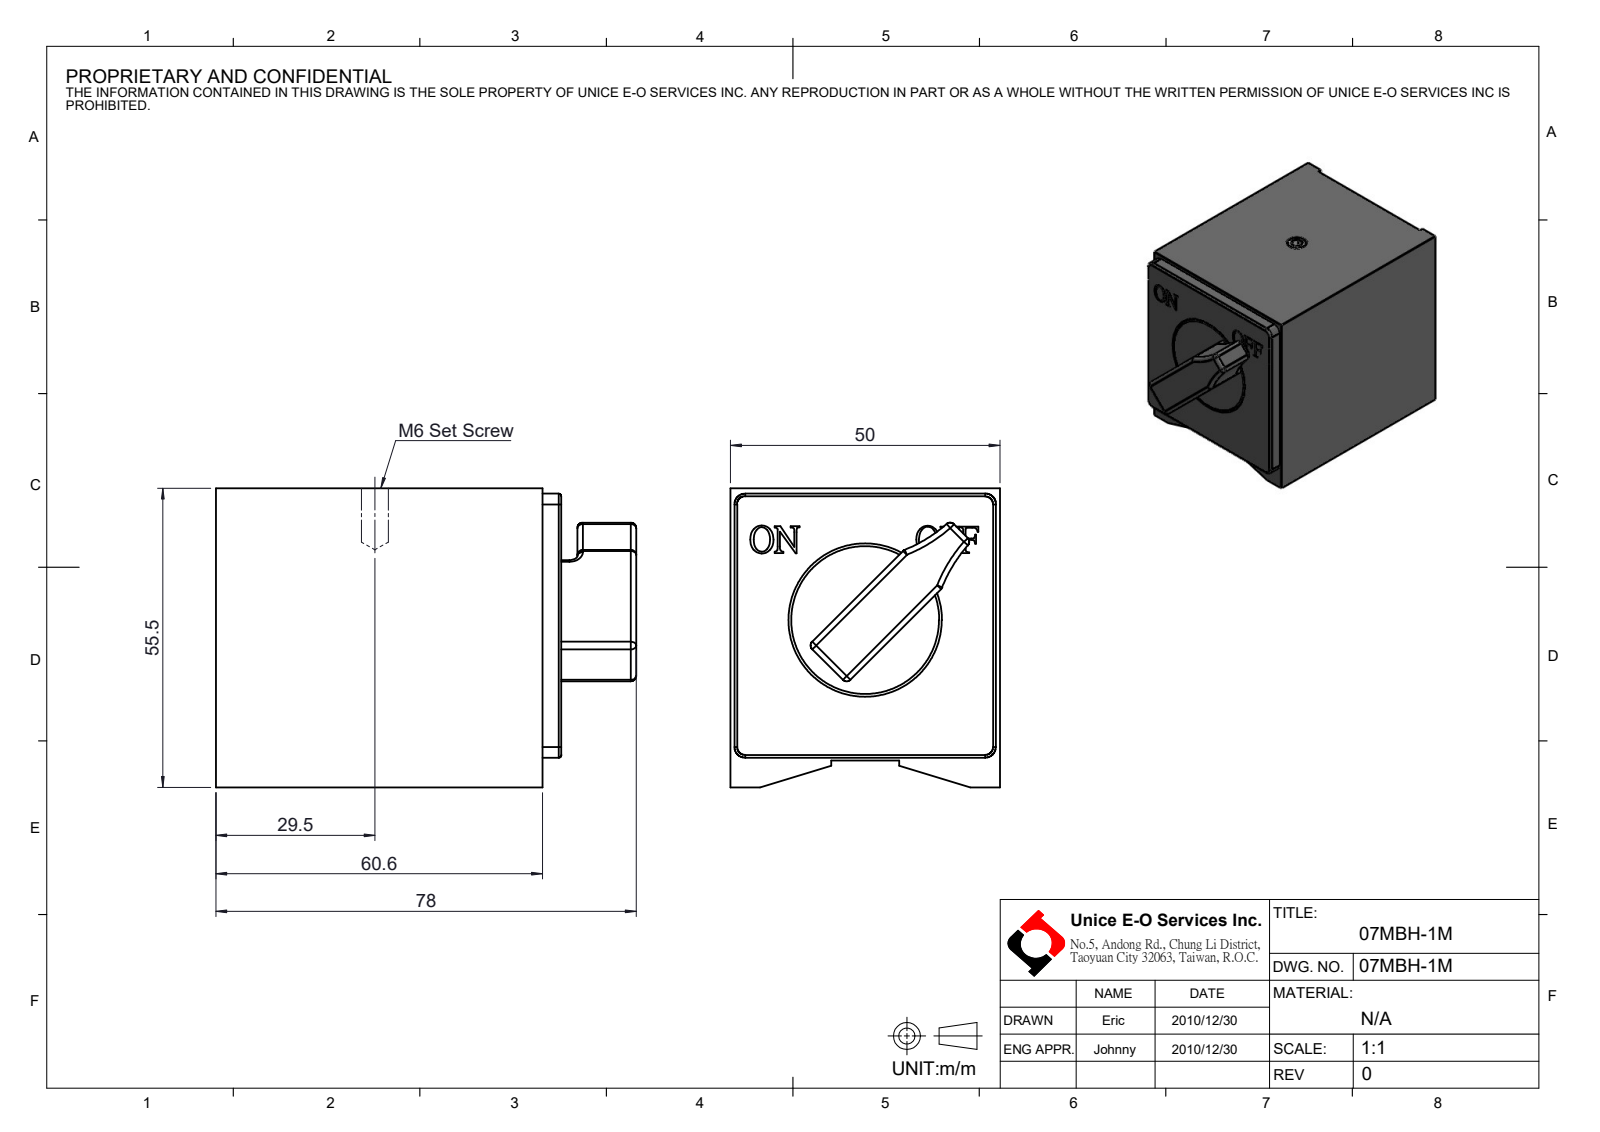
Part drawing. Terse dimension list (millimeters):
name: 07MBH-1M
written by: SolidWorks 2016 (CONFIG_CONTROL_DESIGN)
unit: mm
bodies: 0 solids, 109 faces (49 planar, 31 cylindrical, 29 other)
size: 78 × 55.5 × 50
holes: 1× ⌀28.5
bosses: 1× ⌀27.5
rounds: 15× R1, 4× R0.5, 4× R2, 2× R27.35
face distances: 50, 63.1, 5, 50.5, 1, 55.5, 64.1, 10, 60.6, 59.6
